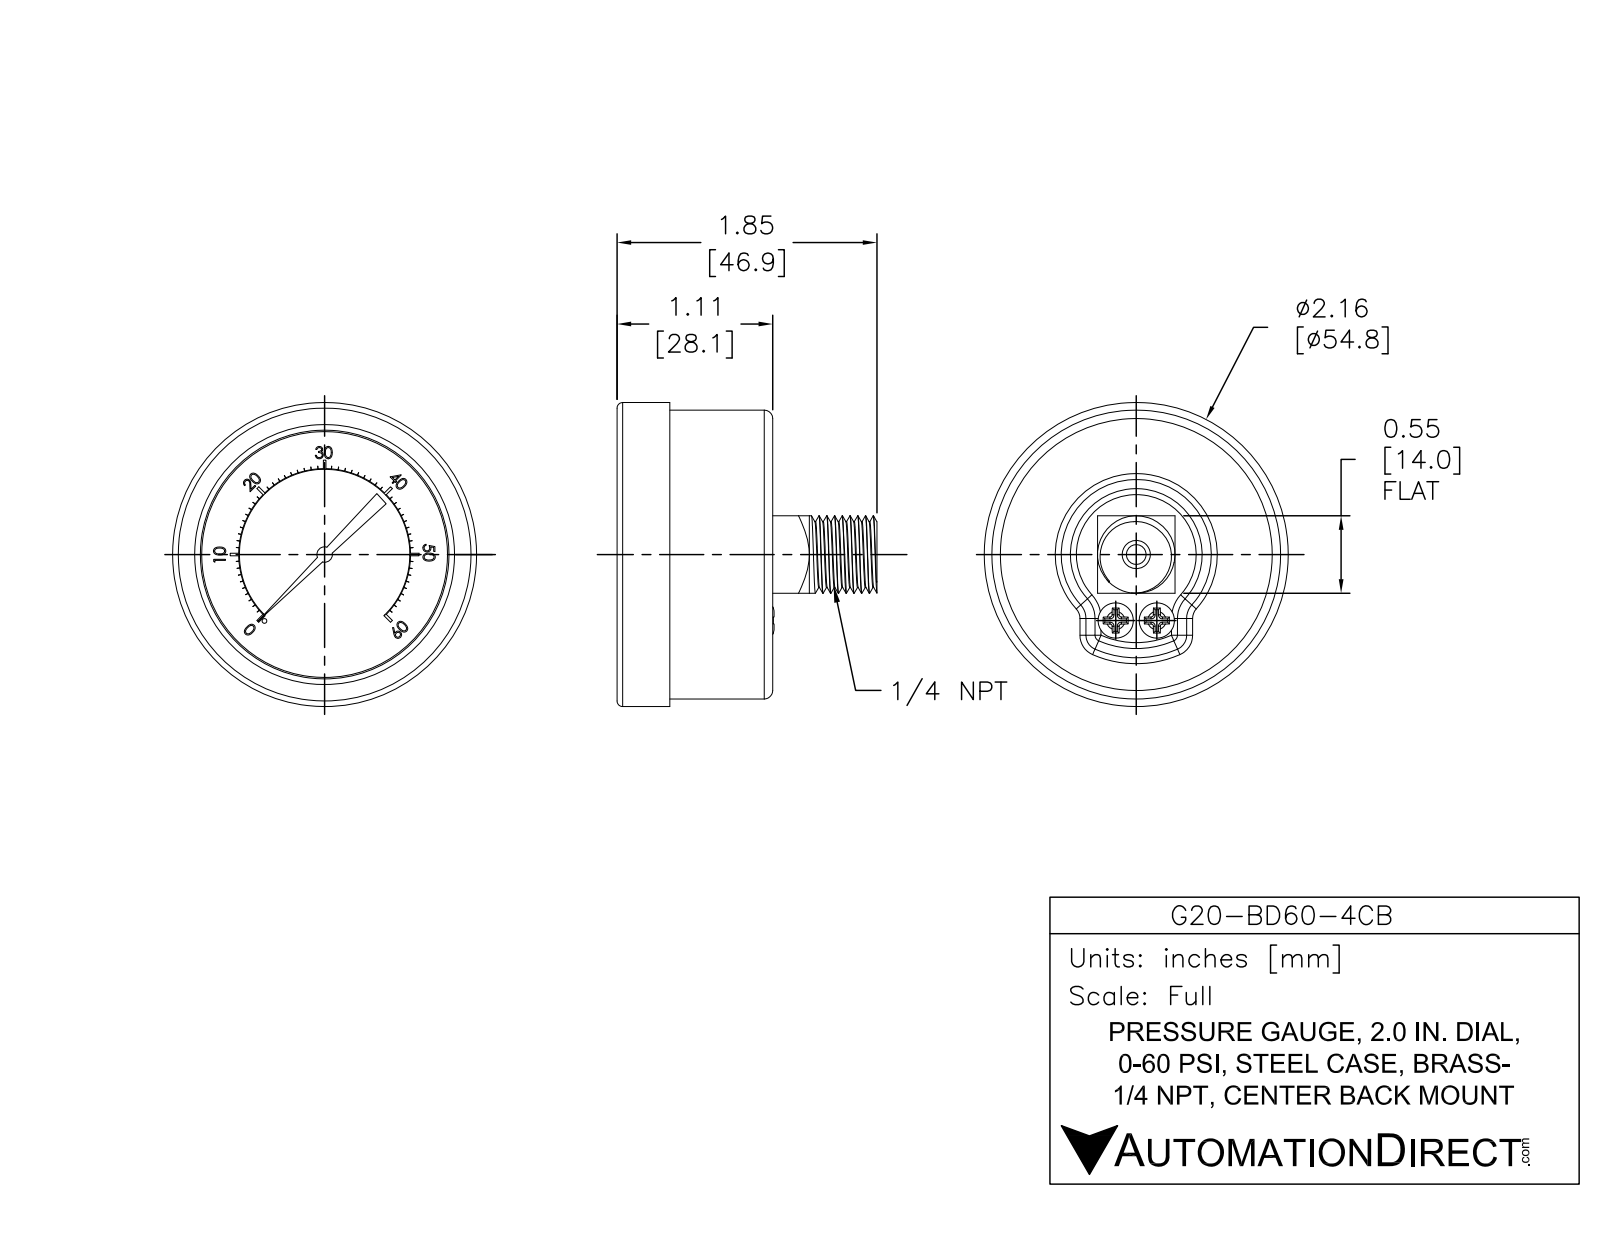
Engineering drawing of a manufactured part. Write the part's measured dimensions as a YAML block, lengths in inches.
part_name: "G20-BD60-4CB"
step_written_by: "SolidWorks 2021 (AUTOMOTIVE_DESIGN)"
units: inches
bodies: {solids: 1, faces: 370, planar: 236, cylindrical: 70, other: 64}
overall_size: [2.158, 2.158, 1.845]
volume: 3.201
surface_area: 18.16
round_holes:
  - {diameter: 0.14, count: 1}
  - {diameter: 1.745, count: 1}
round_bosses_or_shafts:
  - {diameter: 0.25, count: 2}
  - {diameter: 2.158, count: 1}
  - {diameter: 2.05, count: 1}
  - {diameter: 0.55, count: 1}
  - {diameter: 0.11, count: 1}
  - {diameter: 0.102, count: 1}
  - {diameter: 0.055, count: 1}
partial_cylinders:
  - {radius: 0.06, count: 4}
  - {radius: 0.605, count: 1}
  - {radius: 0.61, count: 1}
face_to_face_distances: [0.815, 1.105, 0.29, 0.73, 0.085, 0.375, 0.1, 1.005, 0.63, 0.715]
